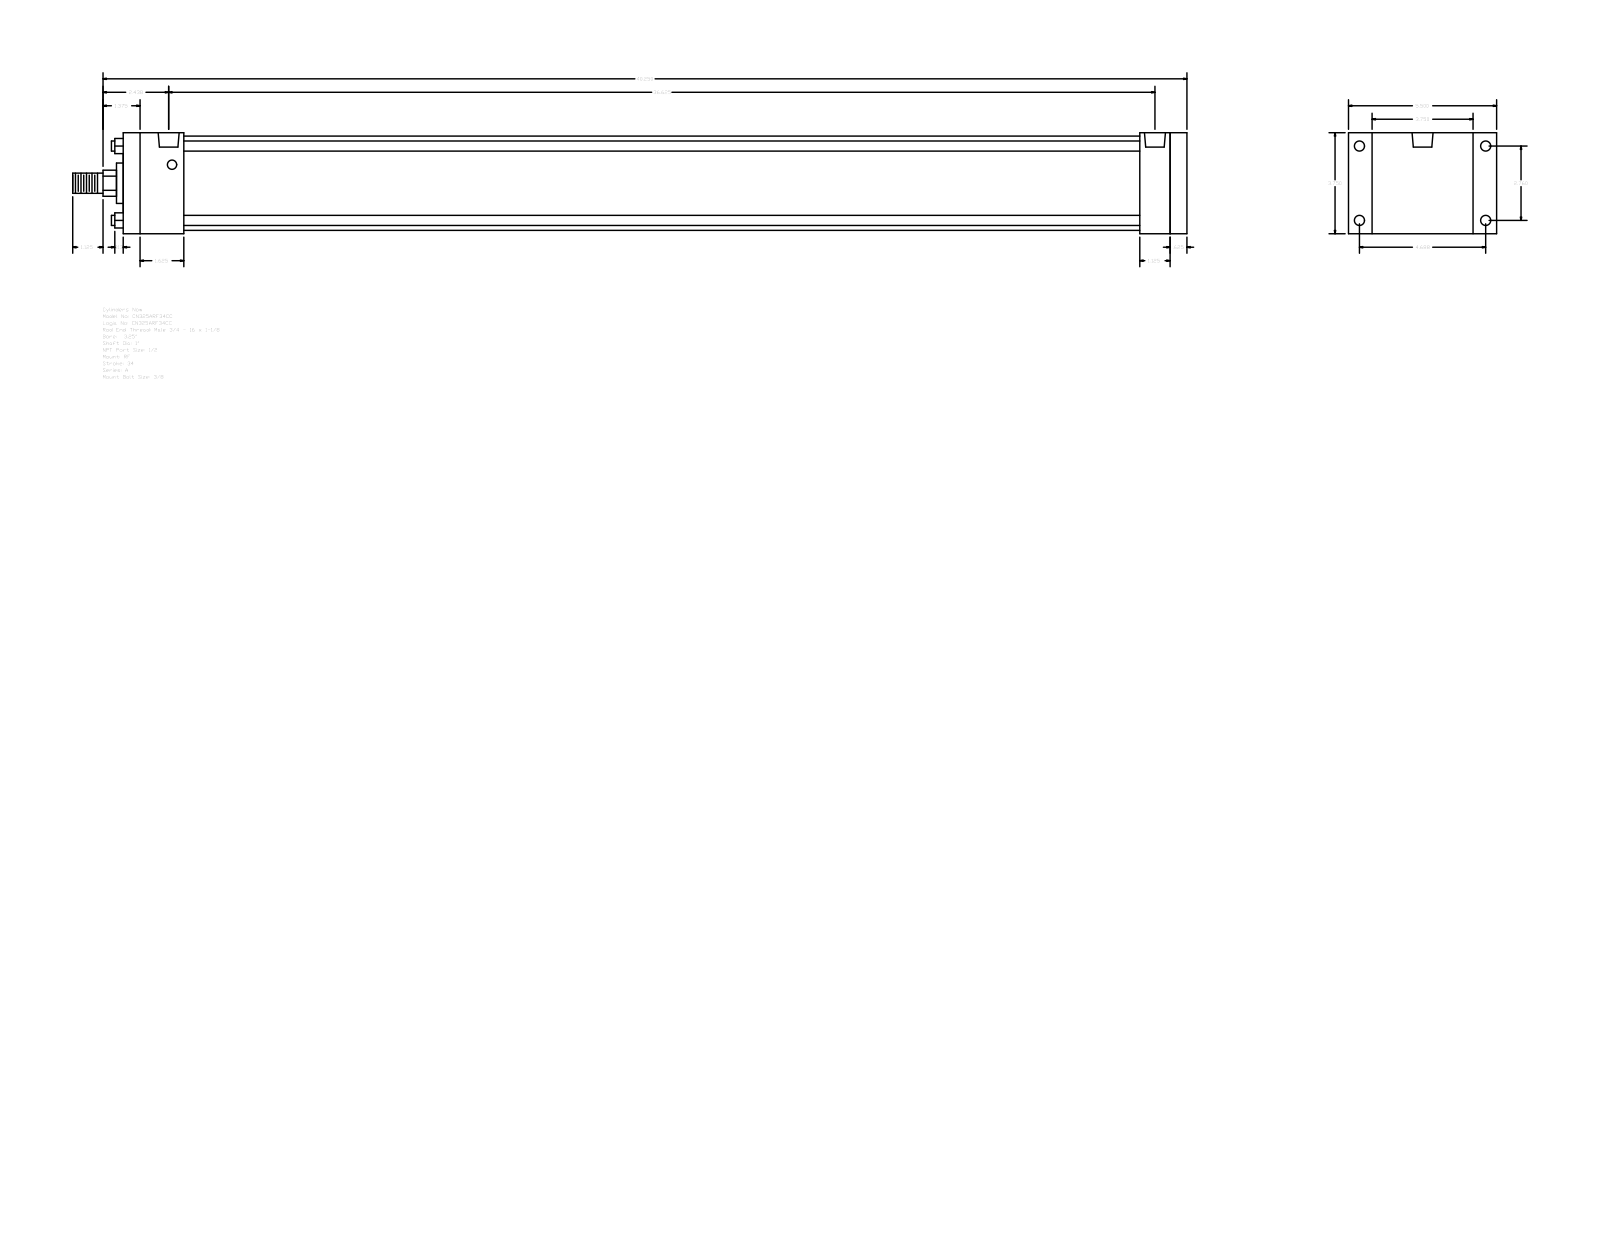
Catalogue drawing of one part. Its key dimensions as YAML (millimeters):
part_name: "A_RF__0325_1"
step_written_by: "GSSL Pune (CONFIG_CONTROL_DESIGN)"
units: millimeters
bodies: {solids: 0, faces: 92, planar: 64, cylindrical: 28, other: 0}
overall_size: [1050.92, 139.7, 95.25]
round_holes:
  - {diameter: 8.73, count: 4}
  - {diameter: 9.53, count: 4}
  - {diameter: 19.77, count: 2}
round_bosses_or_shafts:
  - {diameter: 9.53, count: 4}
  - {diameter: 88.9, count: 1}
  - {diameter: 38.1, count: 1}
  - {diameter: 25.4, count: 1}
  - {diameter: 19.05, count: 1}
partial_cylinders:
  - {radius: 12.29, count: 1}
face_to_face_distances: [95.24, 1003.3, 987.43, 15.87, 22.23, 117.47, 958.85, 28.58, 44.45, 57.15]
hole_center_spacings: [3.18, 70.1, 119.06, 138.16, 923.92, 927.1, 930.28]
